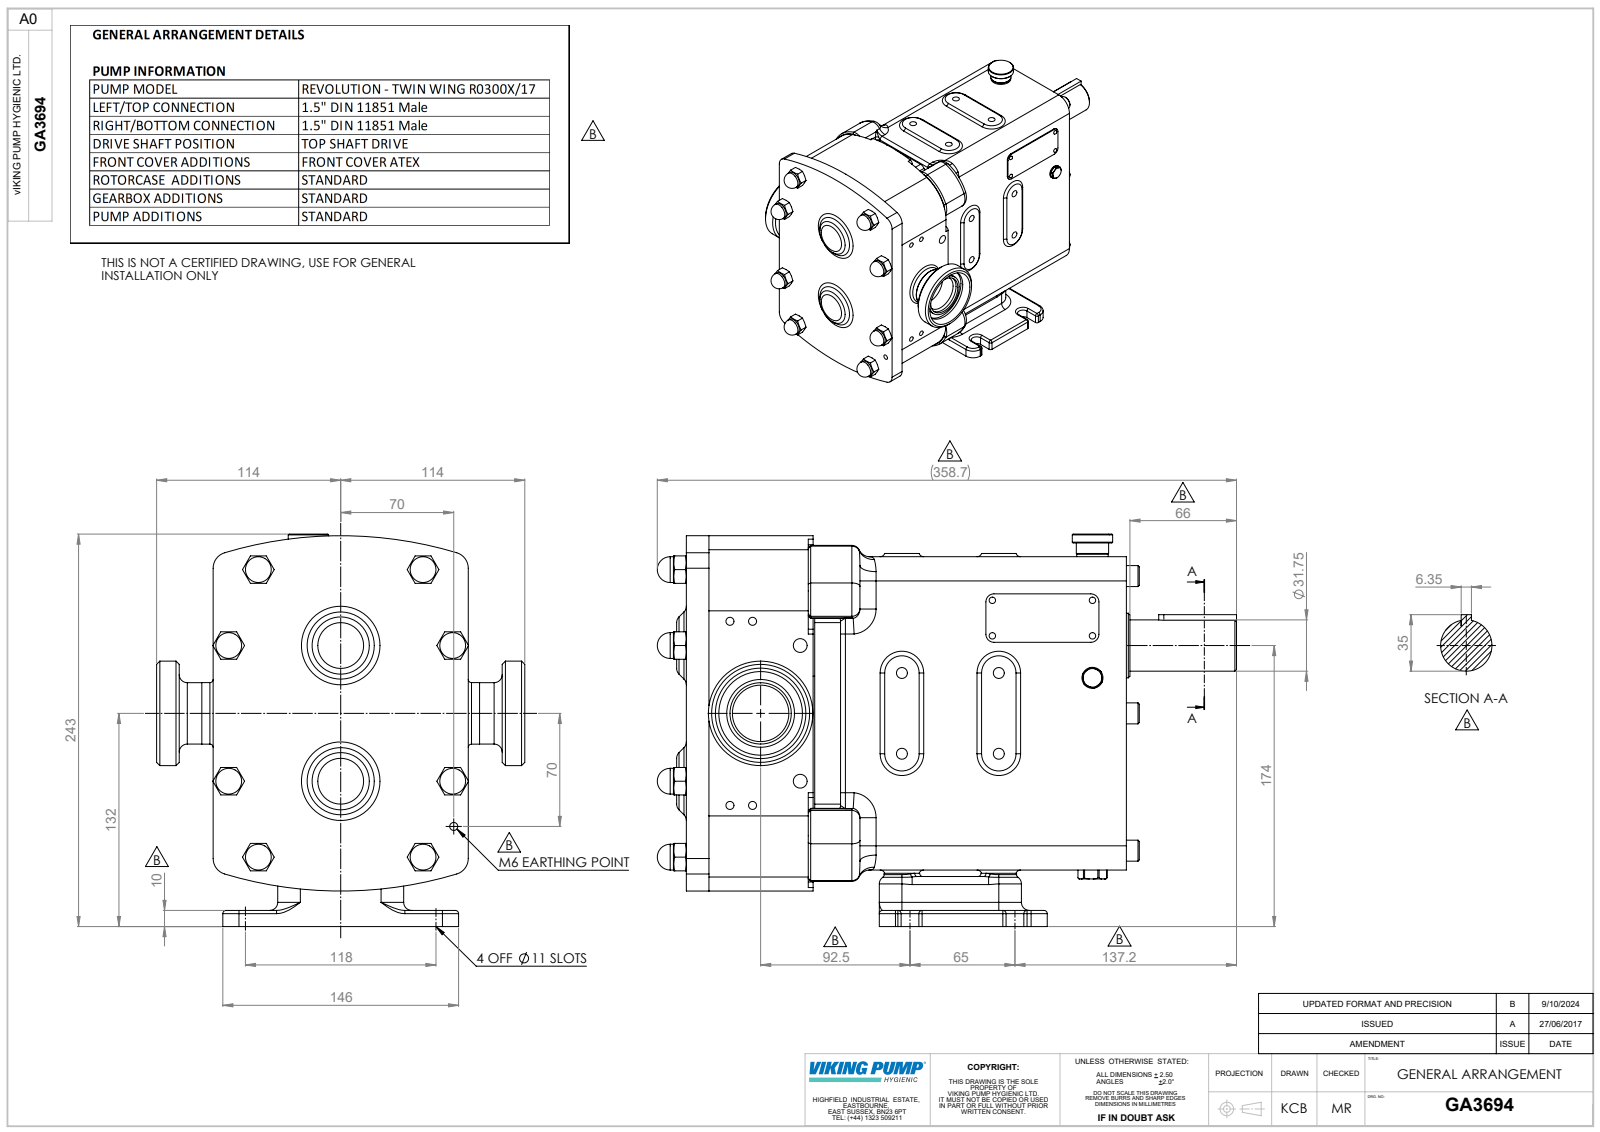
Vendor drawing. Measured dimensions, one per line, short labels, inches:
name: Copy of R0300 CPP H TSD^GA3694; Copy of Z94-5031-22 - 1.5 INCH DIN11851^GA3694; GA3694
written by: SolidWorks 2023 (AUTOMOTIVE_DESIGN)
unit: in
bodies: 3 solids, 989 faces (308 planar, 320 cylindrical, 361 other)
size: 14.122 × 9.567 × 8.976
volume: 427.5 in³; area: 587.7 in²
holes: 8× ⌀0.268, 5× ⌀0.197, 2× ⌀0.337, 1× ⌀0.906, 1× ⌀1.378, 1× ⌀1.496, 1× ⌀2.039
bosses: 8× ⌀0.63, 7× ⌀0.512, 1× ⌀2.547, 1× ⌀1.654, 1× ⌀1.575, 1× ⌀1.5, 1× ⌀1.496, 1× ⌀1.25
rounds: 30× R0.394, 28× R0.118, 24× R0.079, 19× R0.197, 8× R0.232, 8× R0.591, 4× R0.217, 4× R0.315
face distances: 7.638, 0.945, 4.331, 10.728, 5.276, 3.091, 3.13, 7.598, 0.039, 0.157
hole spacings: 1.969, 2.362, 3.075, 0.551, 1.304, 1.812, 1.915, 2.253
